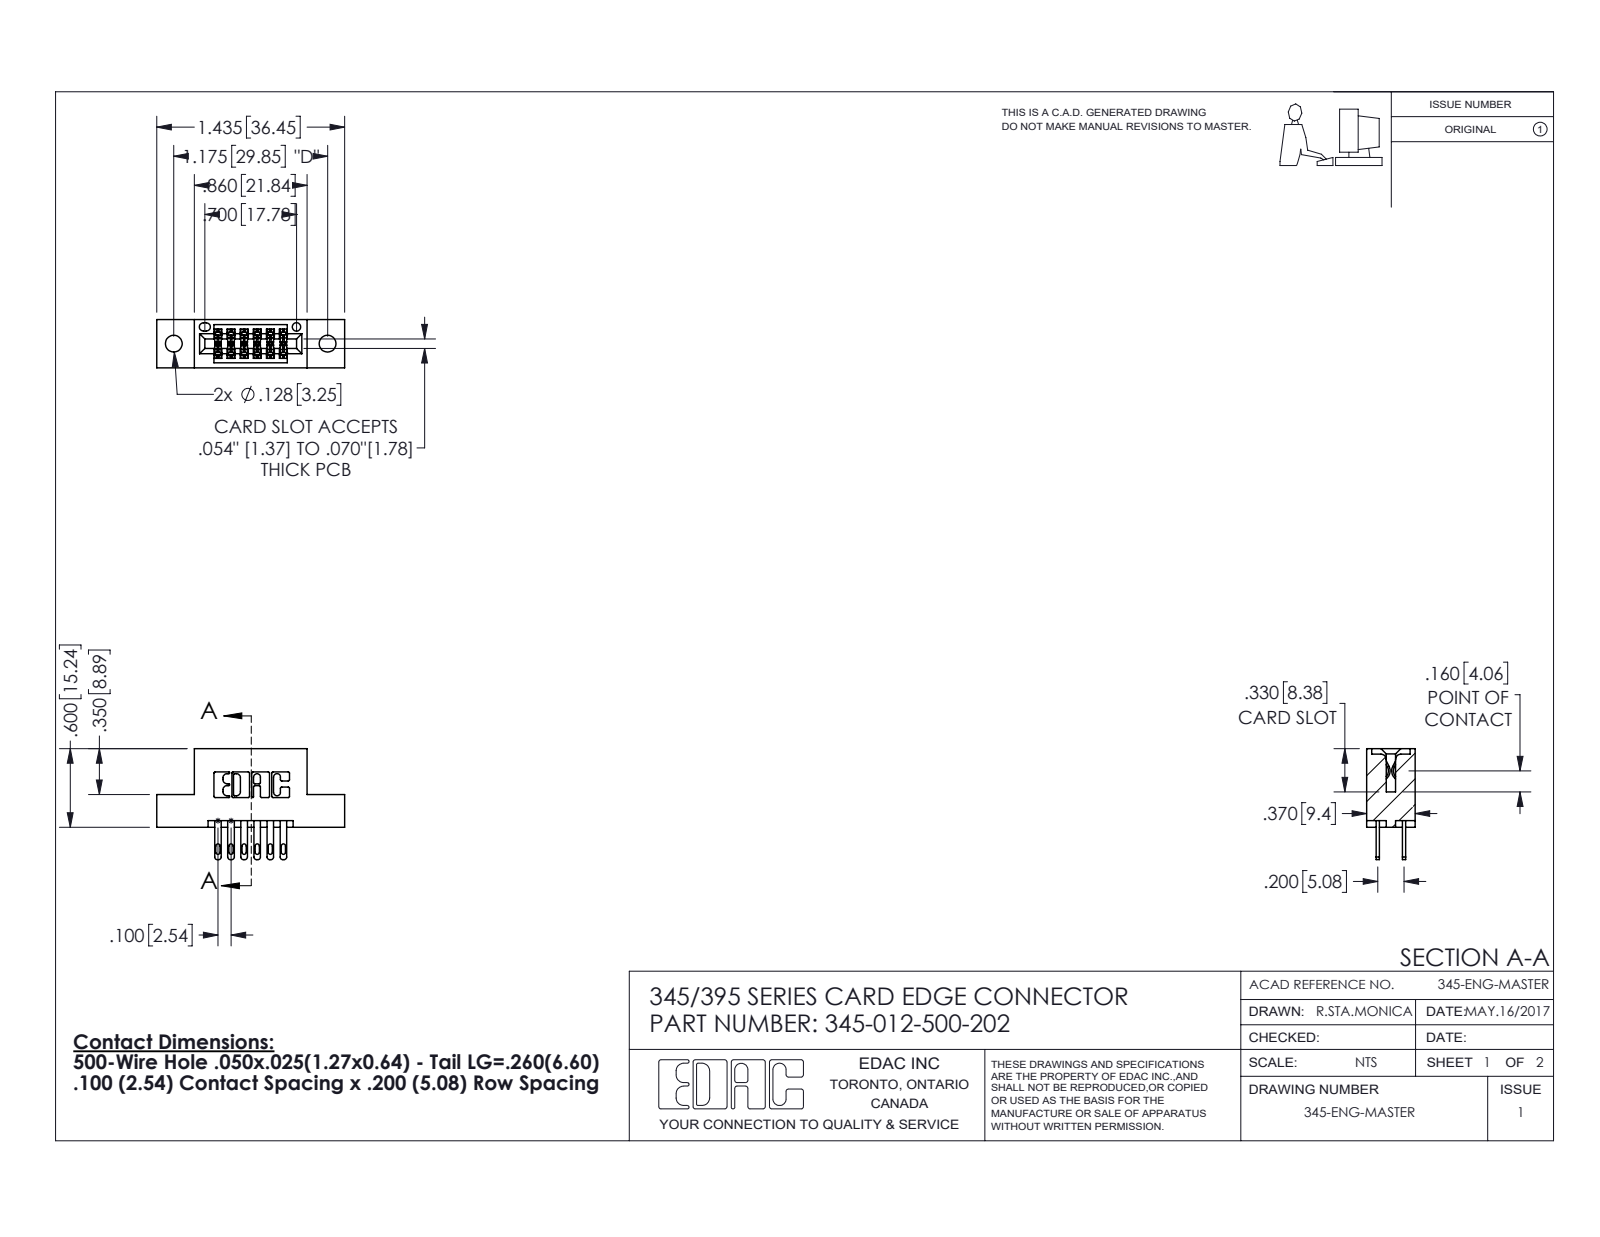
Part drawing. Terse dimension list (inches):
name: 345-292-001_345-293-100; 345 Part_Flush Mounting Lugs - 0.128 Dia; 345-012-500-202
written by: SolidWorks 2016 (CONFIG_CONTROL_DESIGN)
unit: in
bodies: 13 solids, 678 faces (404 planar, 274 cylindrical, 0 other)
size: 1.435 × 0.847 × 0.37
volume: 0.196 in³; area: 6.033 in²
holes: 2× ⌀0.128, 1× ⌀0.064
rounds: 22× R0.01, 18× R0.006, 12× R0.016, 12× R0.02, 6× R0.007, 6× R0.031, 3× R0.026, 2× R0.014
face distances: 0.2, 0.298, 0.072, 0.37, 0.1, 0.098, 0.272, 0.025, 0.225, 0.3
hole spacings: 0.27, 0.946, 1.175
